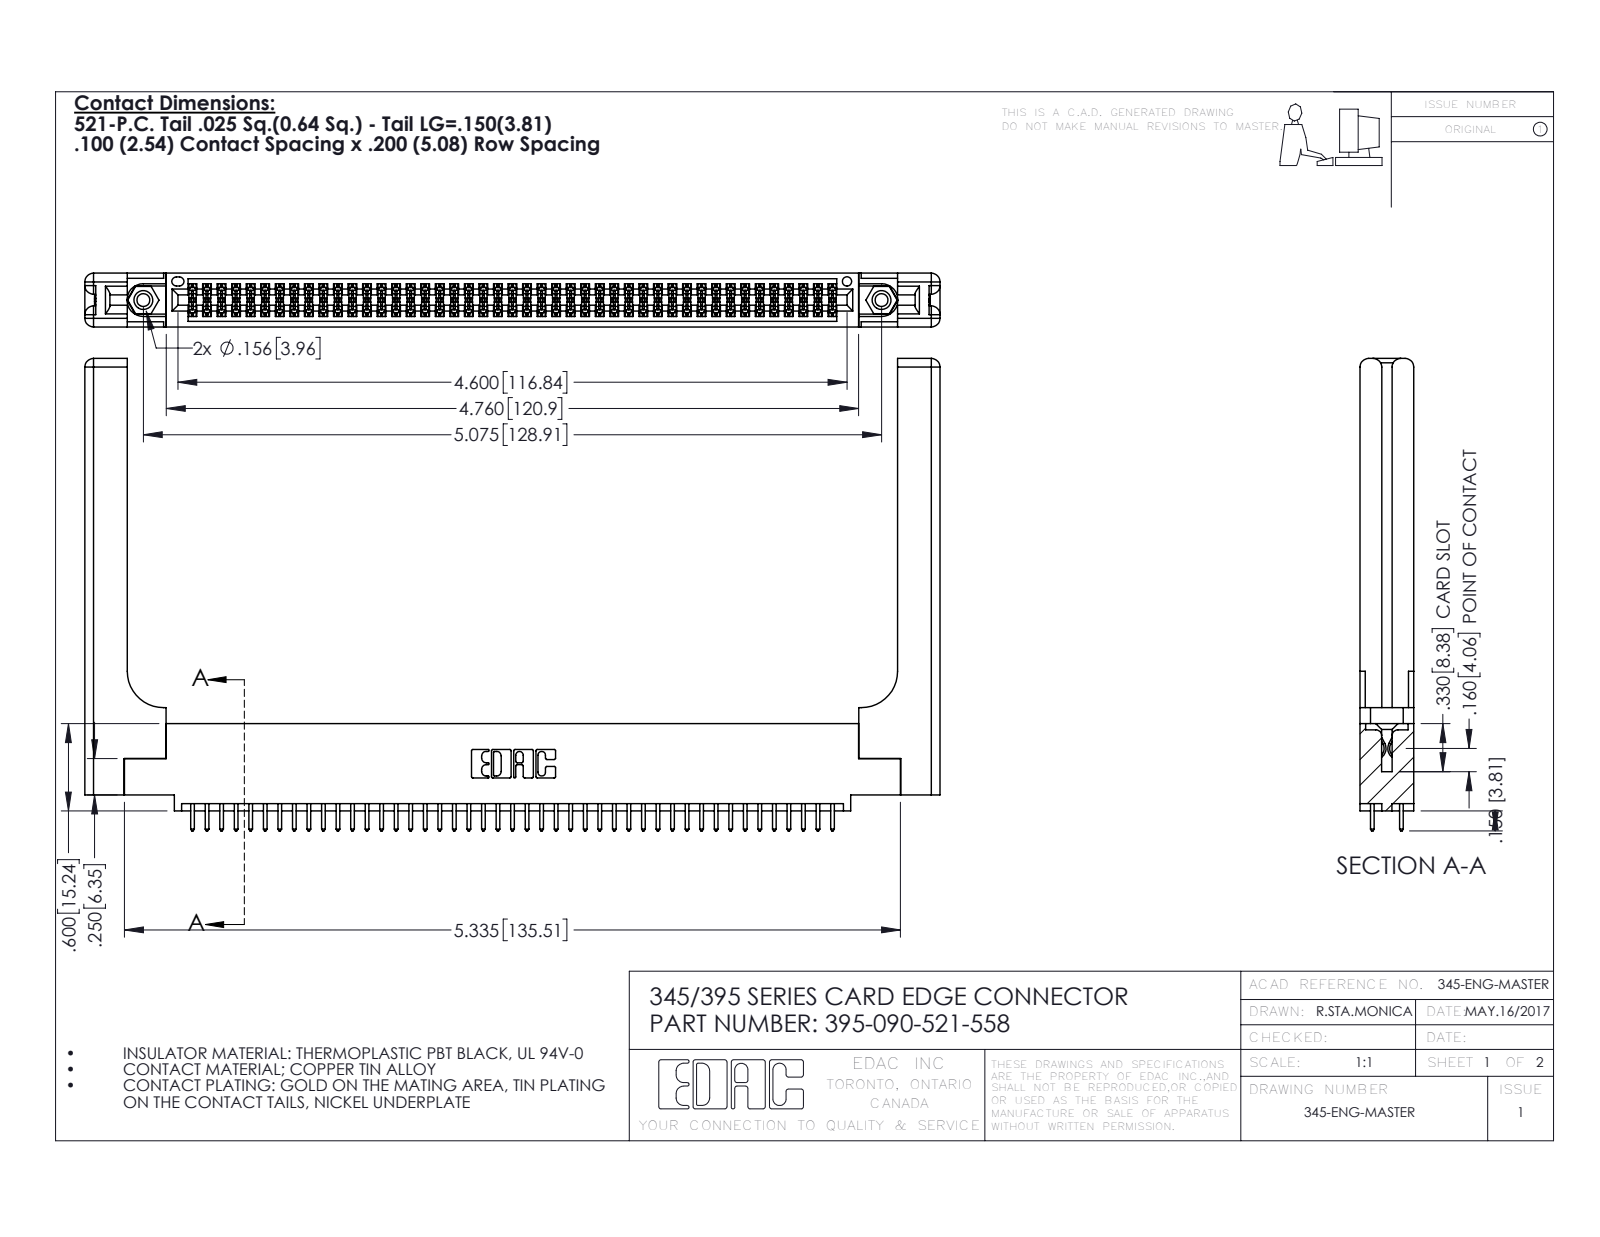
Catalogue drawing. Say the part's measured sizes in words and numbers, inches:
The part is named "345-250-001_345-250-001-102; 395-090-521-558; 345-292-001_345-293-121; 345-220-058_345-220-058 (+1 more)". Its 3-D file was written by "SolidWorks 2016 (CONFIG_CONTROL_DESIGN)". It is 95 solids with 4886 faces: 3202 planar, 1624 cylindrical and 60 other. Overall it measures 5.879 by 3.247 by 0.37 inches. Its volume is 1.397 cubic inches and its surface area 40.75 square inches. Round holes: 2 of diameter 0.089, 2 of diameter 0.125, 2 of diameter 0.156, 1 of diameter 0.064. Round bosses or shafts: 2 of diameter 0.155. Partial cylindrical surfaces (rounded edges, fillets, slot ends): 135 of radius 0.006, 90 of radius 0.01, 22 of radius 0.01, 16 of radius 0.06, 6 of radius 0.007, 6 of radius 0.031, 3 of radius 0.026, 2 of radius 0.014. The main face-to-face distances are 0.072, 0.298, 0.37, 0.098, 0.272, 0.025, 0.2, 0.225, 0.148, 0.15. The hole center spacings are 0.27, 4.839, 5.075.
